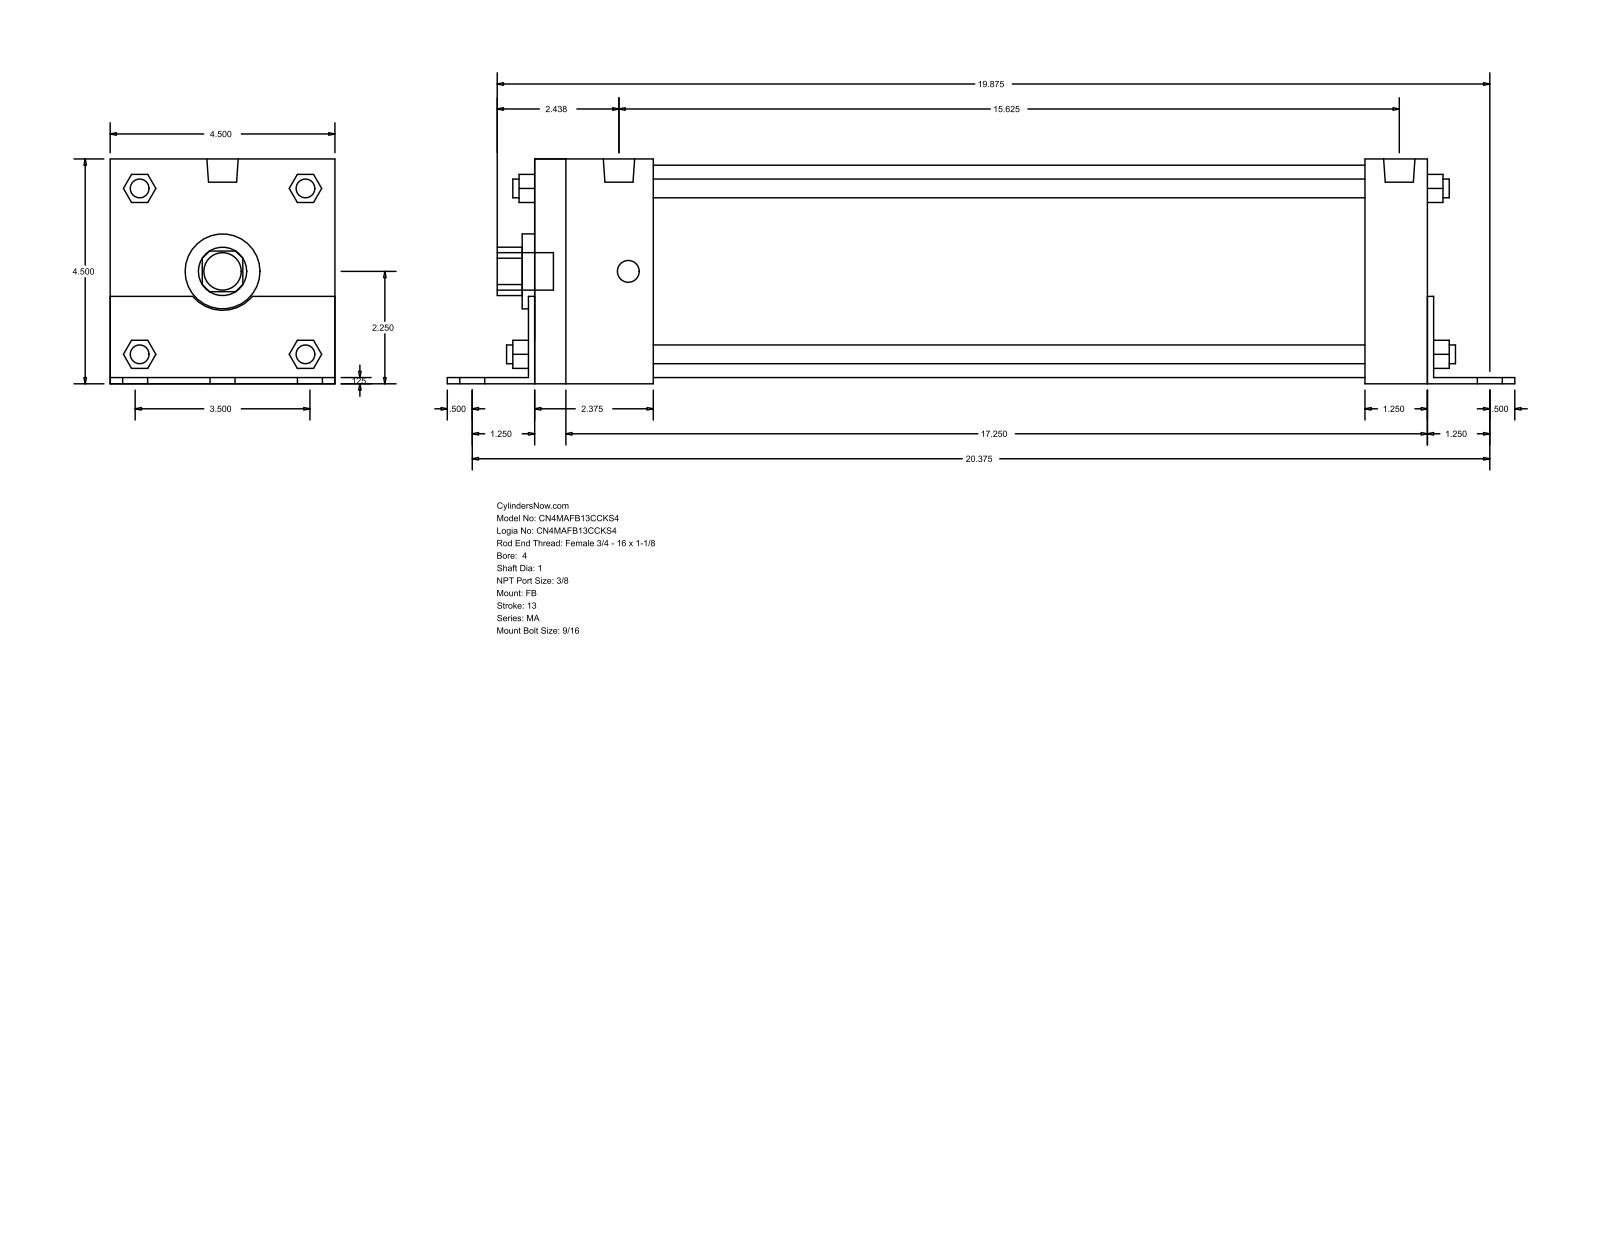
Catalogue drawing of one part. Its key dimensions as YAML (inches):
part_name: "MA_FB__0400_1"
step_written_by: "GSSL Pune (CONFIG_CONTROL_DESIGN)"
units: inches
bodies: {solids: 0, faces: 140, planar: 105, cylindrical: 35, other: 0}
overall_size: [21.375, 4.502, 4.5]
round_holes:
  - {diameter: 1, count: 1}
  - {diameter: 1.5, count: 1}
  - {diameter: 4.25, count: 1}
round_bosses_or_shafts:
  - {diameter: 0.563, count: 6}
  - {diameter: 0.437, count: 4}
  - {diameter: 0.375, count: 4}
  - {diameter: 0.627, count: 2}
  - {diameter: 0.75, count: 1}
partial_cylinders:
  - {radius: 0.484, count: 1}
  - {radius: 0.78, count: 1}
face_to_face_distances: [4.5, 0.125, 4.502, 0.123, 4.377, 17.875, 0.125, 18.125, 18, 18]
